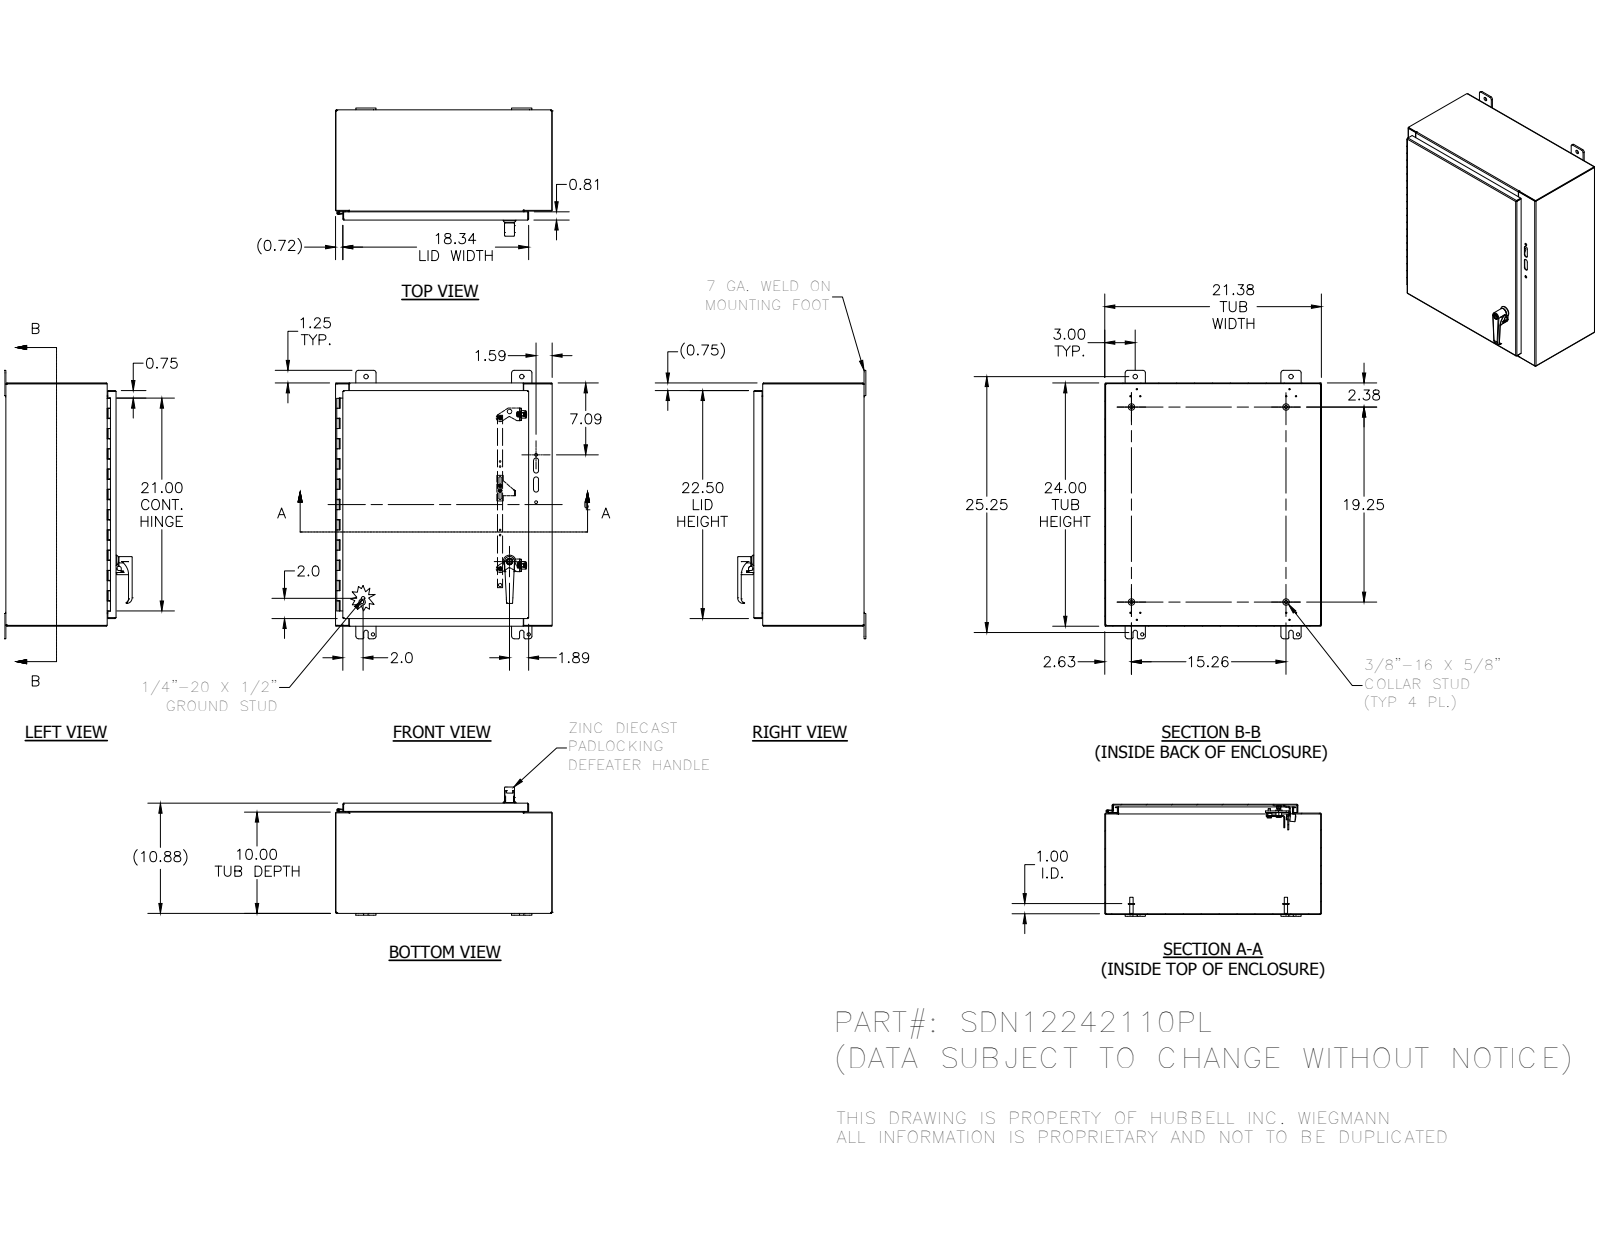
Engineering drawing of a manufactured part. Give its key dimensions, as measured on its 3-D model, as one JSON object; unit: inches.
{"part_name": "SDN12242110PL", "step_written_by": "SolidWorks 2019 (AUTOMOTIVE_DESIGN)", "units": "inches", "bodies": {"solids": 49, "faces": 1545, "planar": 792, "cylindrical": 525, "other": 228}, "overall_size": [26.5, 21.38, 12.649], "volume_in3": 166.9, "surface_area_in2": 4439, "round_holes": [[0.12, 12], [0.145, 6], [0.313, 4], [0.438, 4], [0.32, 3], [0.156, 2], [0.196, 2], [0.211, 2], [0.22, 2], [0.281, 2], [0.313, 2], [0.45, 2]], "round_bosses_or_shafts": [[0.33, 5], [0.437, 4], [0.3, 4], [0.25, 4], [0.19, 4], [0.625, 3], [0.225, 3], [0.75, 2]], "partial_cylinders_radius": [[0.02, 38], [0.012, 31], [0.25, 22], [0.031, 20], [0.105, 20], [0.125, 17], [0.025, 16], [0.07, 8]], "face_to_face_distances": [0.074, 10.801, 21.306, 23.926, 10.727, 10.875, 9.926, 0.875, 21.38, 21.232], "hole_center_spacings": [0.759, 14.752, 14.9, 15.38, 21.38, 21.402, 22.068, 22.075]}
